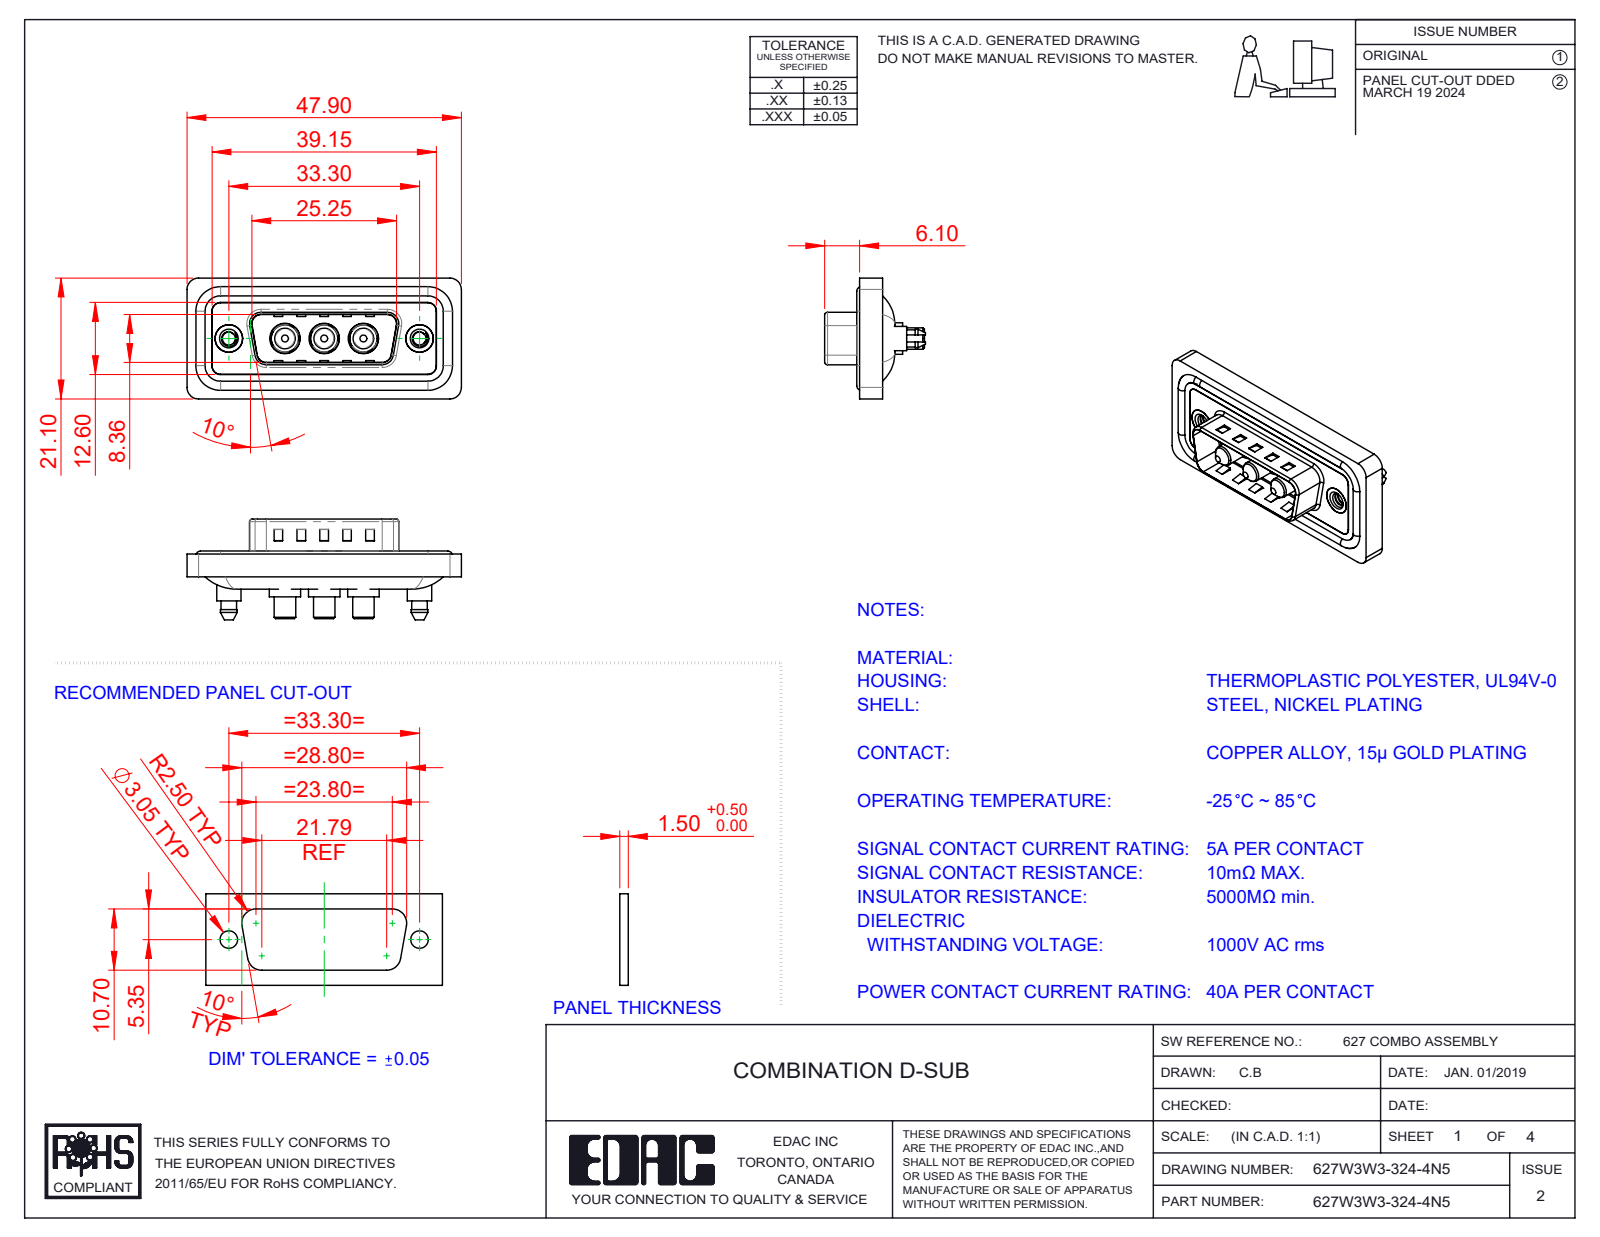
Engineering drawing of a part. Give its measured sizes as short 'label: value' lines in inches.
name: 627Combo Shell Front_15 Contacts; 627Combo Waterproof Housing_15 Contacts; 627W3W3-324-4N5; 627Combo Housing_3W3 (+3 more)
written by: SolidWorks 2023 (CONFIG_CONTROL_DESIGN)
unit: in
bodies: 13 solids, 614 faces (223 planar, 273 cylindrical, 118 other)
size: 1.886 × 0.831 × 0.693
volume: 0.352 in³; area: 14.13 in²
holes: 3× ⌀0.191, 3× ⌀0.209, 2× ⌀0.089, 2× ⌀0.157, 2× ⌀0.189, 2× ⌀0.197
bosses: 4× ⌀0.063, 3× ⌀0.217, 3× ⌀0.205, 3× ⌀0.187, 3× ⌀0.148, 3× ⌀0.142, 2× ⌀0.213, 2× ⌀0.193
rounds: 28× R0.059, 20× R0.079, 10× R0.063, 8× R0.02, 4× R0.01, 4× R0.024, 4× R0.026, 4× R0.035
face distances: 0.016, 0.043, 0.122, 0.059, 0.063, 0.02, 0.114, 0.157, 0.028, 0.032
hole spacings: 0.27, 0.386, 0.656, 0.925, 0.539, 1.311
